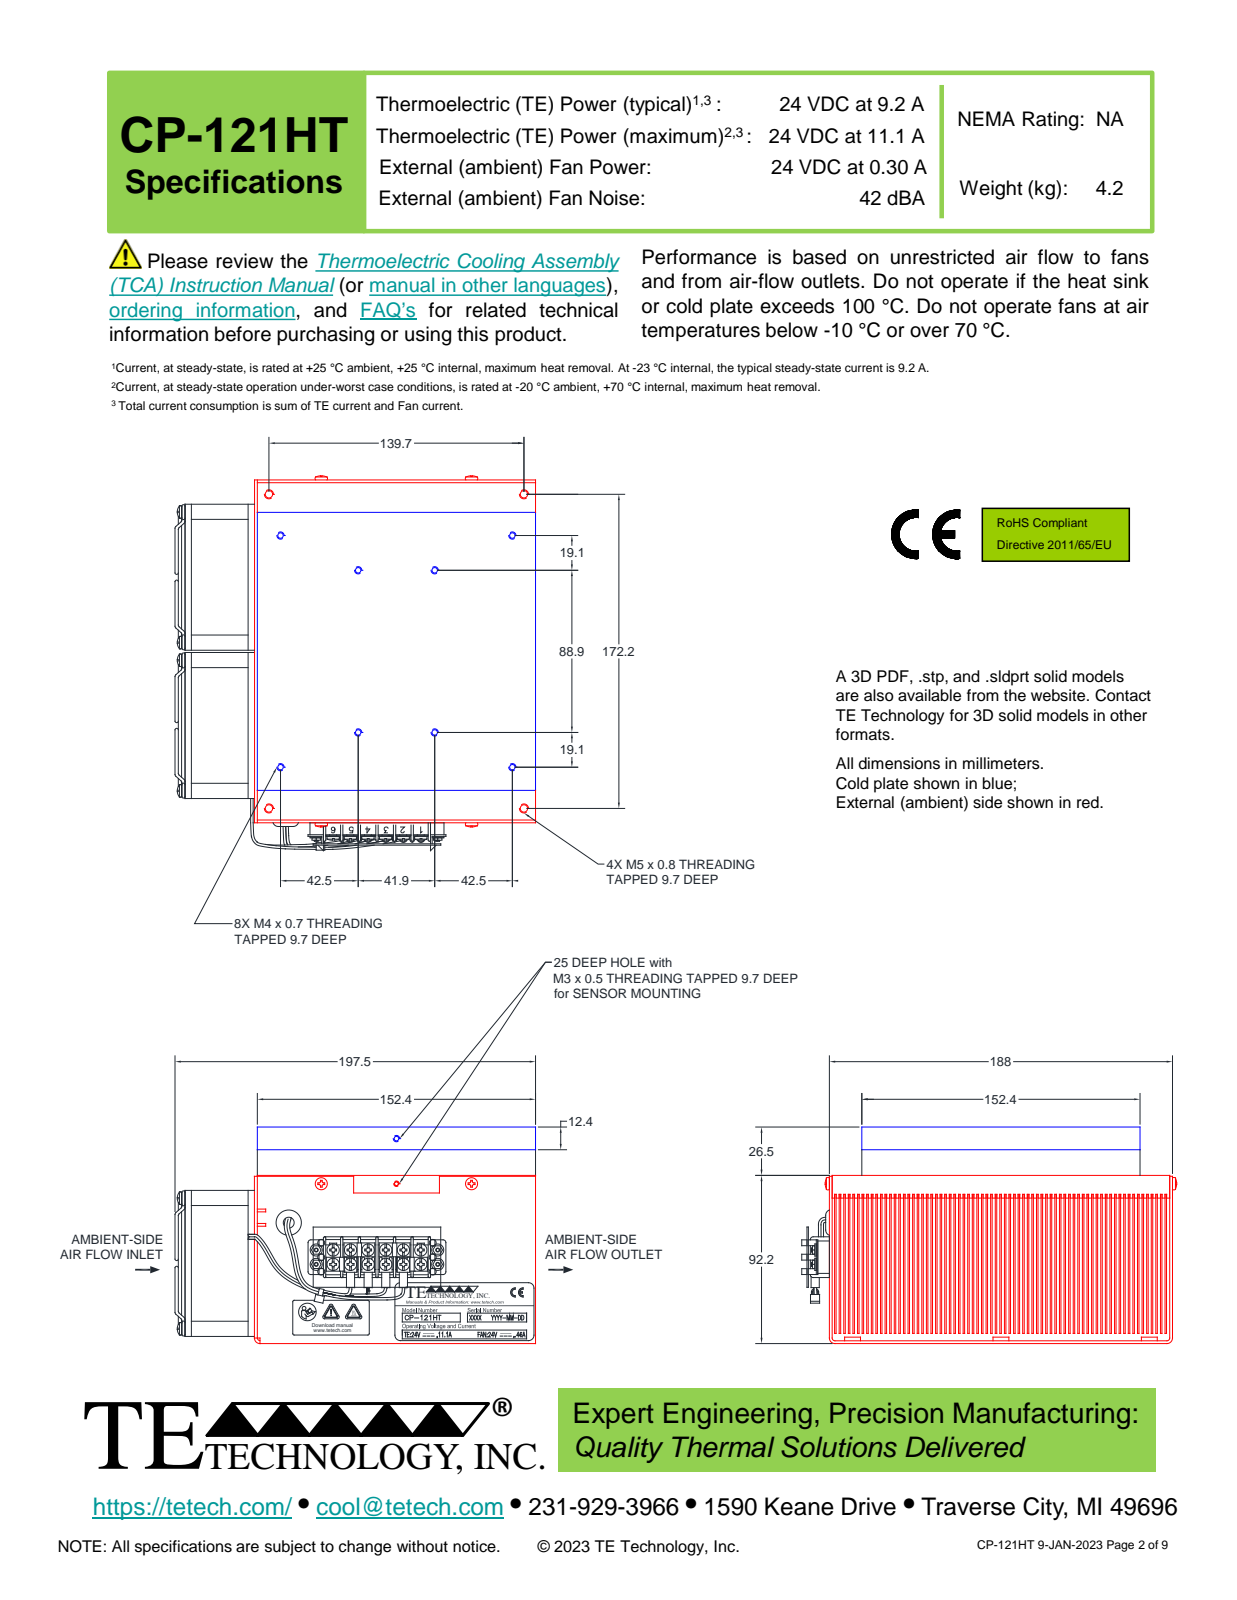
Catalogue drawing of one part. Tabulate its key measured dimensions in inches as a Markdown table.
| quantity | value |
| --- | --- |
| part name | cold plate CP-121HT; gasket CP-121HT; heat sink CP-121HT; dummy module 39 tall no wires (+8 more) |
| STEP written by | Alibre (AUTOMOTIVE_DESIGN) |
| units | inches |
| bodies | 197 solids, 4113 faces (2301 planar, 783 cylindrical, 1029 other) |
| overall size | 8.098 × 7.776 × 4.724 |
| volume | 110.3 in³ |
| surface area | 2 825 in² |
| round holes (diameter × count) | 0.104 × 20, 0.163 × 12, 0.104 × 8, 0.128 × 8, 0.177 × 8, 0.187 × 8, 0.25 × 8, 0.252 × 8, 0.164 × 6, 0.166 × 6, 0.168 × 6, 0.17 × 6 |
| round bosses / shafts (diameter × count) | 0.138 × 28, 0.27 × 22, 0.071 × 19, 0.056 × 19, 0.072 × 14, 0.344 × 8, 0.297 × 8, 0.28 × 8 |
| partial cylindrical surfaces (radius × count) | 0.038 × 21, 0.031 × 16, 0.015 × 8, 0.03 × 8, 0.031 × 8, 0.032 × 8, 0.078 × 8, 0.118 × 8 |
| main face-to-face distances | 0.1, 0.2, 0.3, 0.063, 0.032, 0.068, 0.168, 0.4, 0.132, 1.094 |
| hole center spacings | 0.31, 0.75, 0.812, 1.991, 2.815, 0.375, 0.487, 4.08 |
